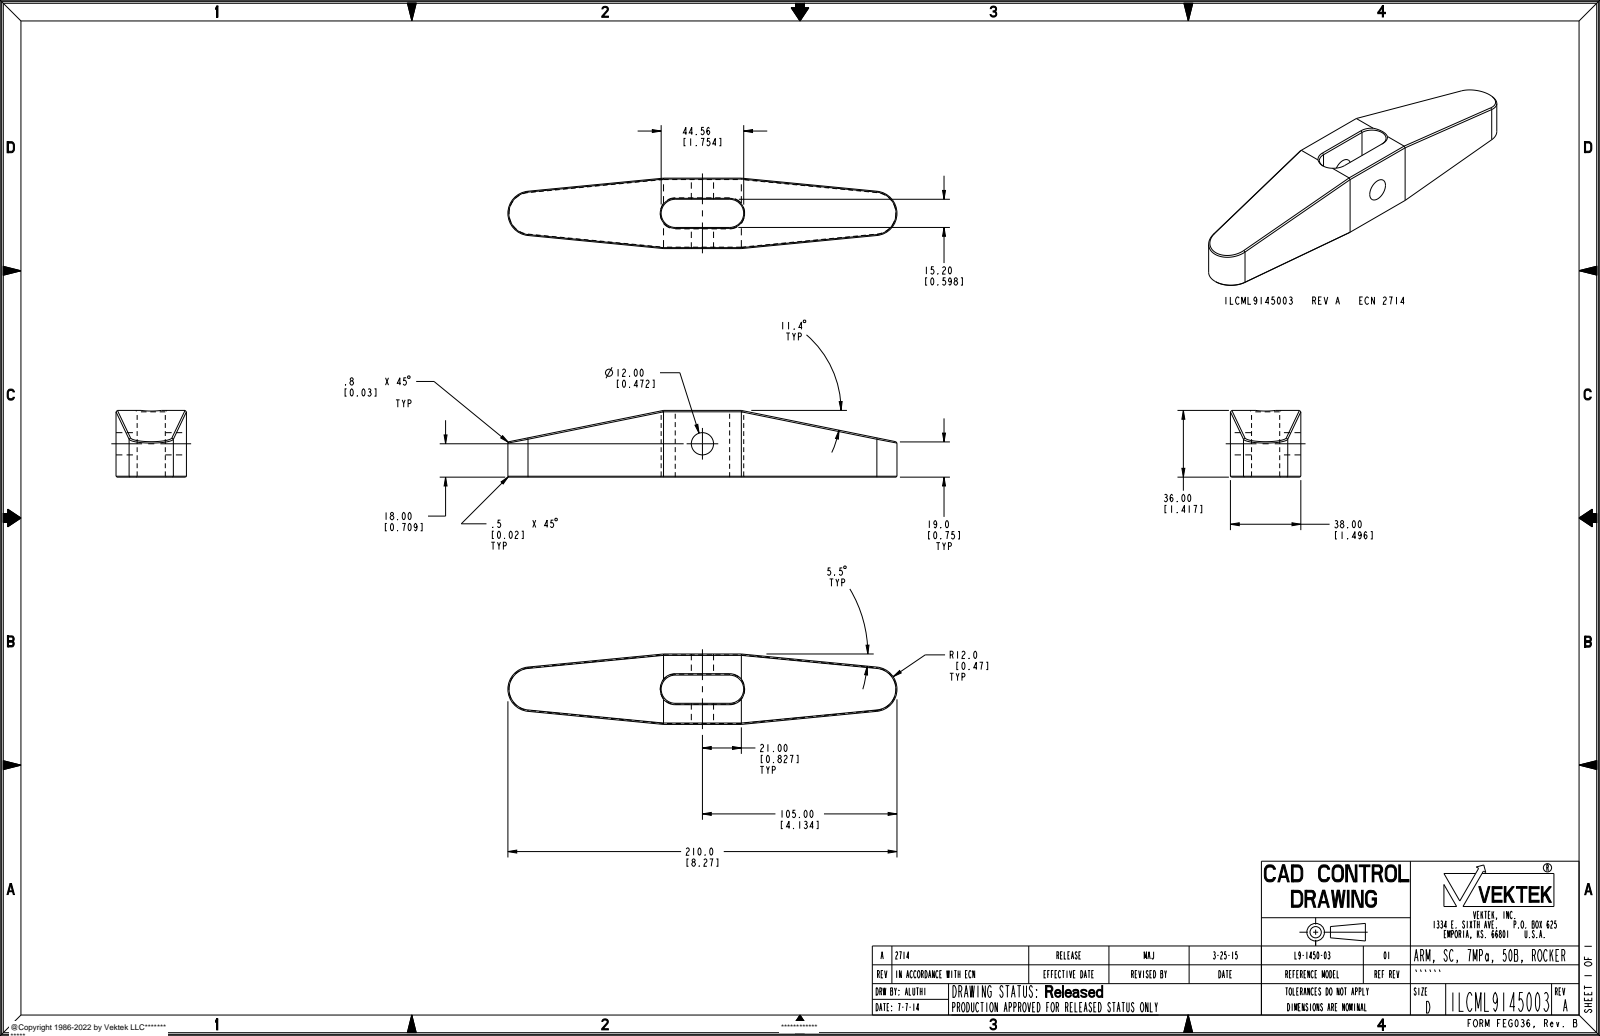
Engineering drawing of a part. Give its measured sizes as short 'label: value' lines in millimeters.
name: ILCML9145003
written by: PRO/ENGINEER BY PARAMETRIC TECHNOLOGY CORPORATION, 2013320 (AUTOMOTIVE_DESIGN)
unit: mm
bodies: 1 solid, 45 faces (29 planar, 8 cylindrical, 8 other)
size: 210 × 38 × 36
volume: 172 127 mm³; area: 28 554 mm²
holes: 1× ⌀12
rounds: 2× R7.6, 2× R12
face distances: 41.84, 11.4, 26.6, 38, 15.2, 36, 18.8, 51.42, 32.62, 32.61
